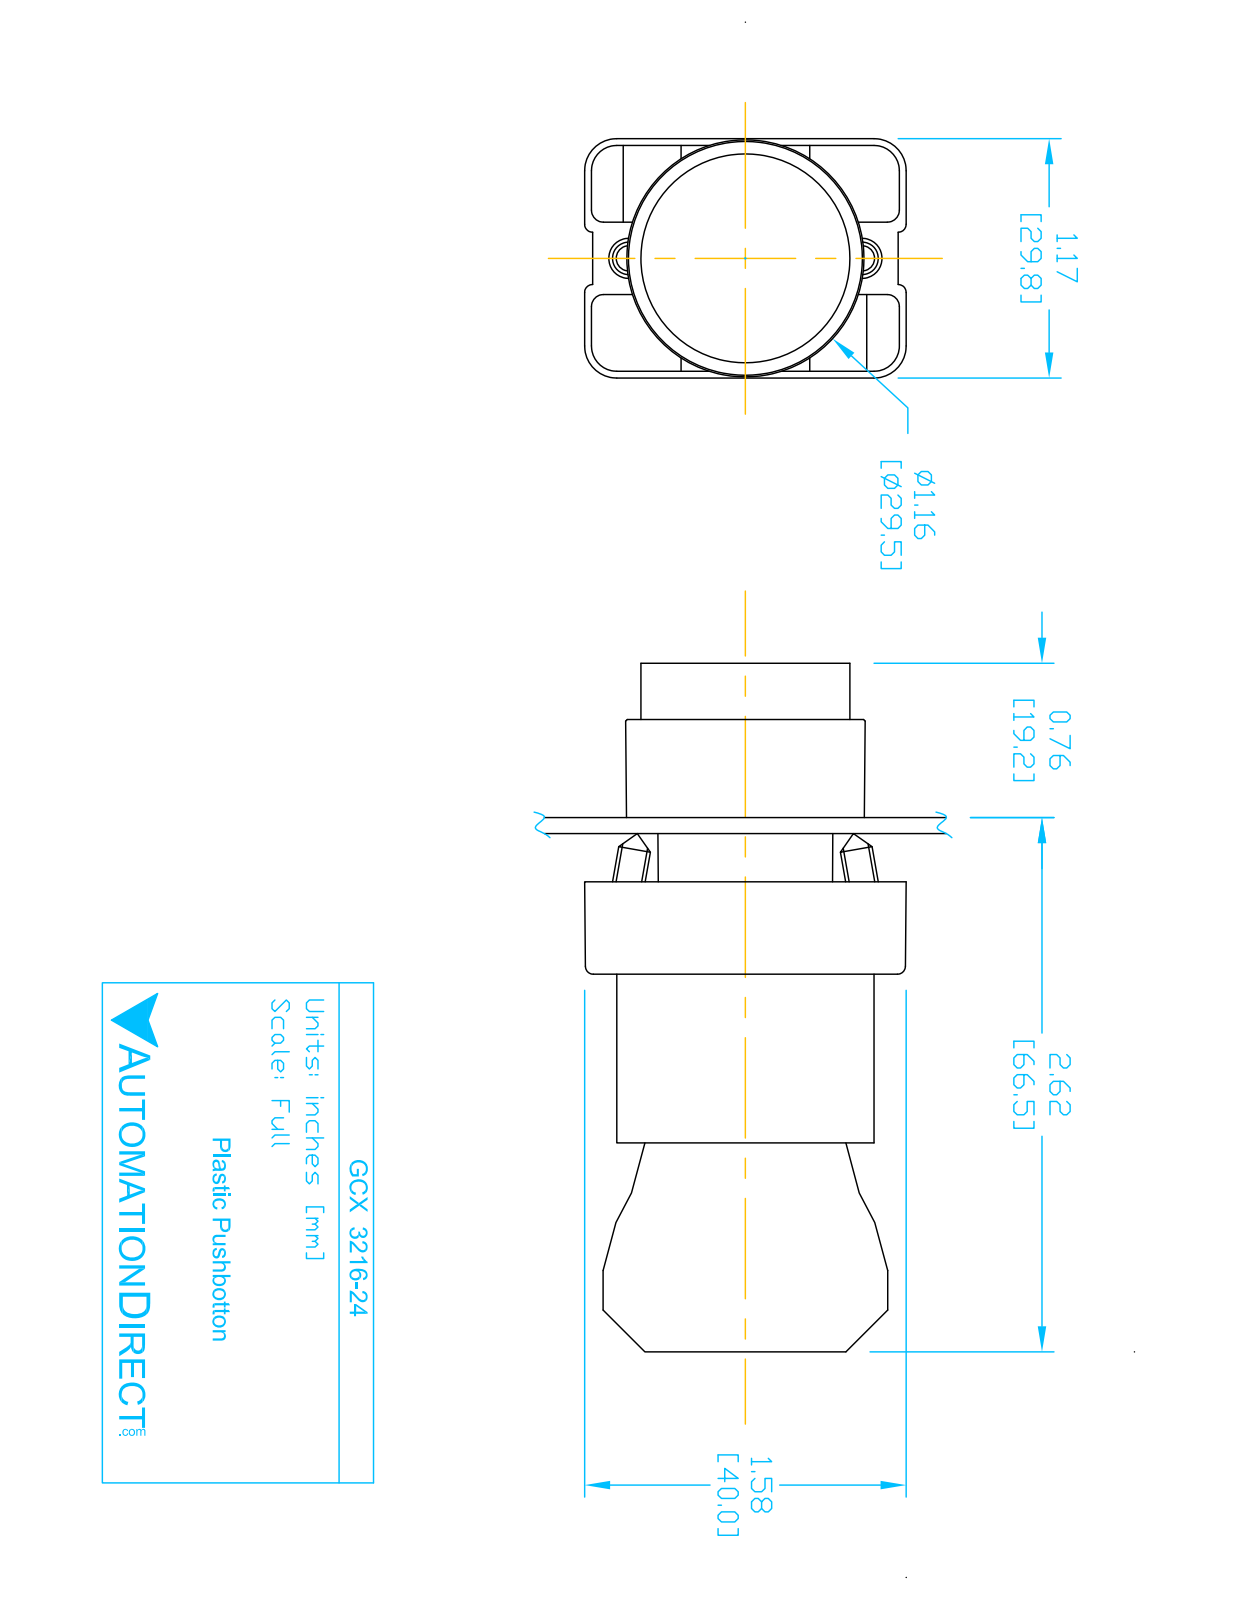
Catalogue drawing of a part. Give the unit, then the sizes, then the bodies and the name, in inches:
Units: inches
Overall size (bounding box): 3.319 × 1.581 × 1.177
Round holes (diameter × count): ⌀0.079 ×2, ⌀0.124 ×2, ⌀0.13 ×2, ⌀0.087 ×1, ⌀0.197 ×1, ⌀0.469 ×1, ⌀0.878 ×1, ⌀0.888 ×1, ⌀1.024 ×1
Round bosses / shafts (diameter × count): ⌀0.157 ×4, ⌀1.175 ×1, ⌀1.004 ×1, ⌀0.945 ×1, ⌀0.856 ×1, ⌀0.78 ×1, ⌀0.504 ×1
Partial cylindrical surfaces — rounded edges, fillets, slot ends (radius × count): R0.059 ×24, R0.041 ×12, R0.124 ×12, R0.157 ×12, R0.039 ×8, R0.128 ×2, R0.02 ×1, R0.063 ×1
Main face-to-face distances: 0.827, 0.579, 1.171, 2.02, 1.193, 0.031, 0.033, 0.573, 1.165, 0.593
Hole centre spacings: 0.236, 0.544, 0.472, 0.49
Volume: 2.721 in³ · Surface area: 36.32 in²
Bodies: 7 solids, 425 faces (250 planar, 144 cylindrical, 31 other)
Part name (STEP PRODUCT): GCX3216-24; ECX3029-2; ECX1050; GCX3216 OPERATOR (+1 more)
STEP written by: SolidWorks 2016 (AUTOMOTIVE_DESIGN)
